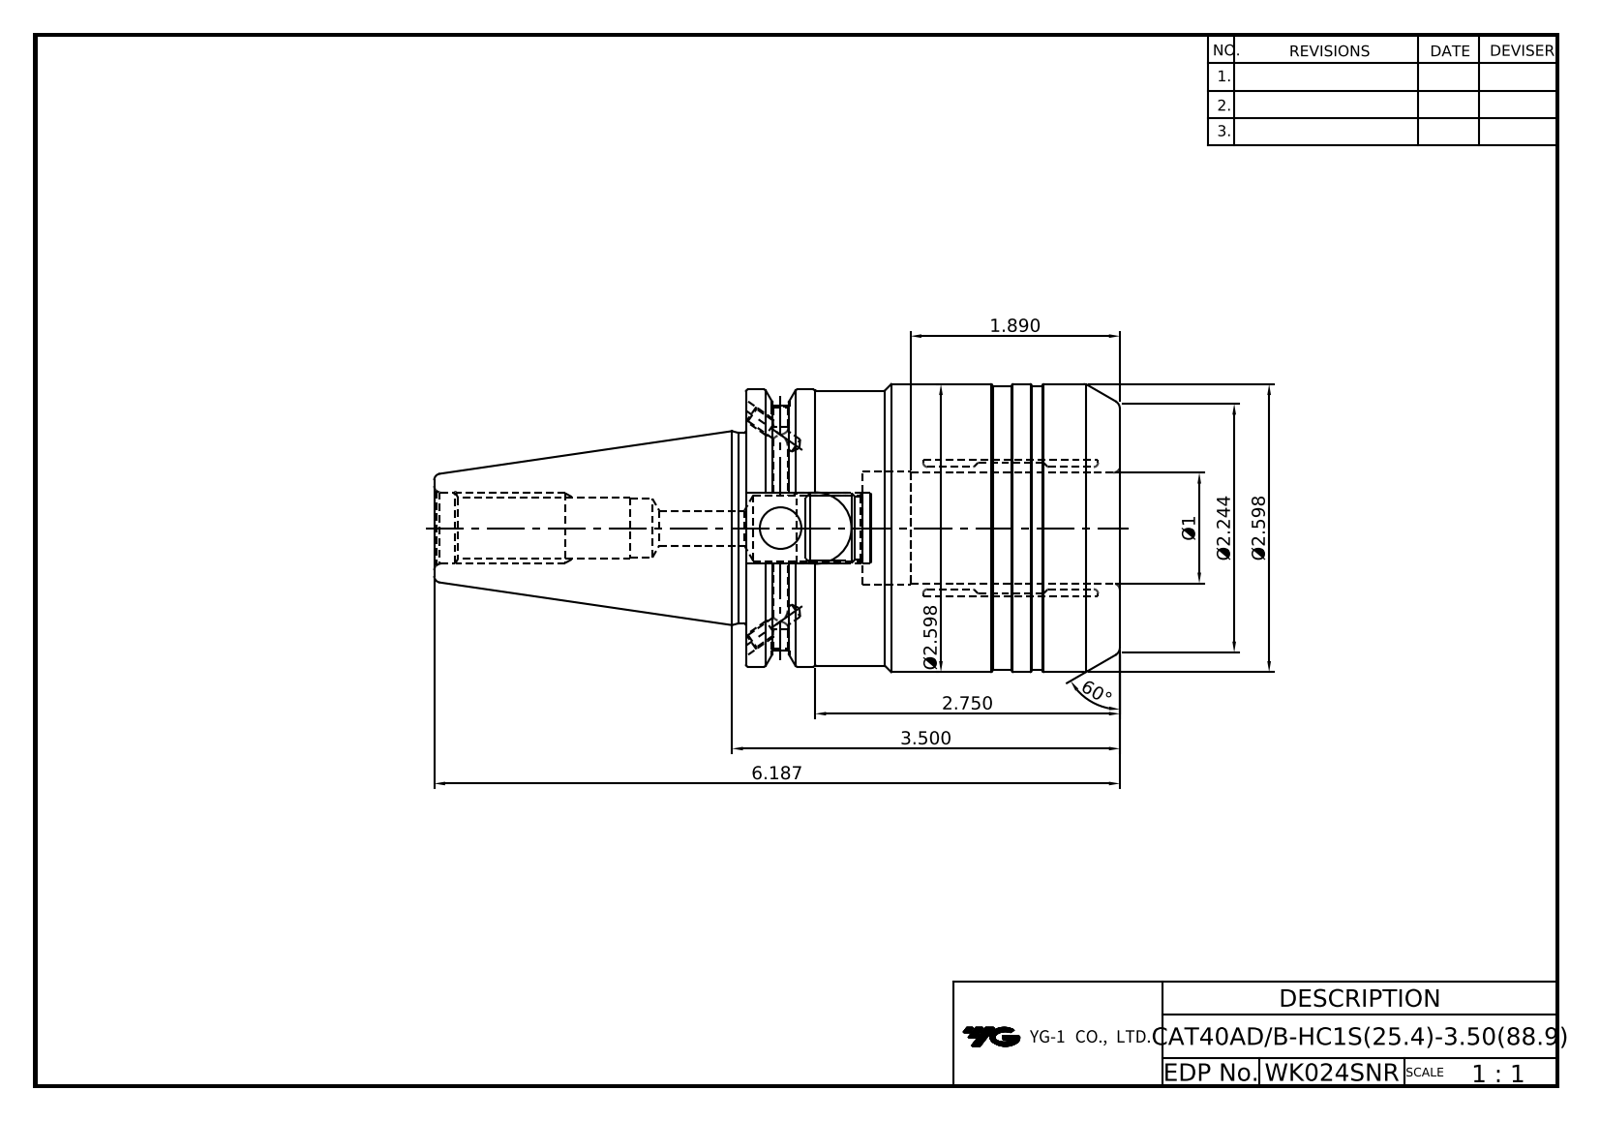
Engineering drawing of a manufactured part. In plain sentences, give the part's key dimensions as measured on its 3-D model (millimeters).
The part is named "LO-CAT40ADB-HC25.4S-88.9". Its 3-D file was written by "Autodesk Inventor 2020 (AUTOMOTIVE_DESIGN)". It is 1 solid with 108 faces: 35 planar, 37 cylindrical and 36 other. Overall it measures 157.15 by 66 by 66 millimeters. Its volume is 297 963 cubic millimeters and its surface area 40 629 square millimeters. Round holes: 4 of diameter 3.24, 2 of diameter 4, 2 of diameter 4.2, 1 of diameter 8, 1 of diameter 9.53, 1 of diameter 13, 1 of diameter 13.39, 1 of diameter 14.92, 1 of diameter 16.3, 1 of diameter 25.4, 1 of diameter 25.8. Round bosses or shafts: 1 of diameter 66, 1 of diameter 65, 1 of diameter 63.5, 1 of diameter 63, 1 of diameter 43.6. Partial cylindrical surfaces (rounded edges, fillets, slot ends): 1 of radius 8.19, 1 of radius 28.15. The main face-to-face distances are 85.73, 26.73, 59, 47.6, 16.38, 71.42, 98.15, 157.15, 81.3, 9.88.
